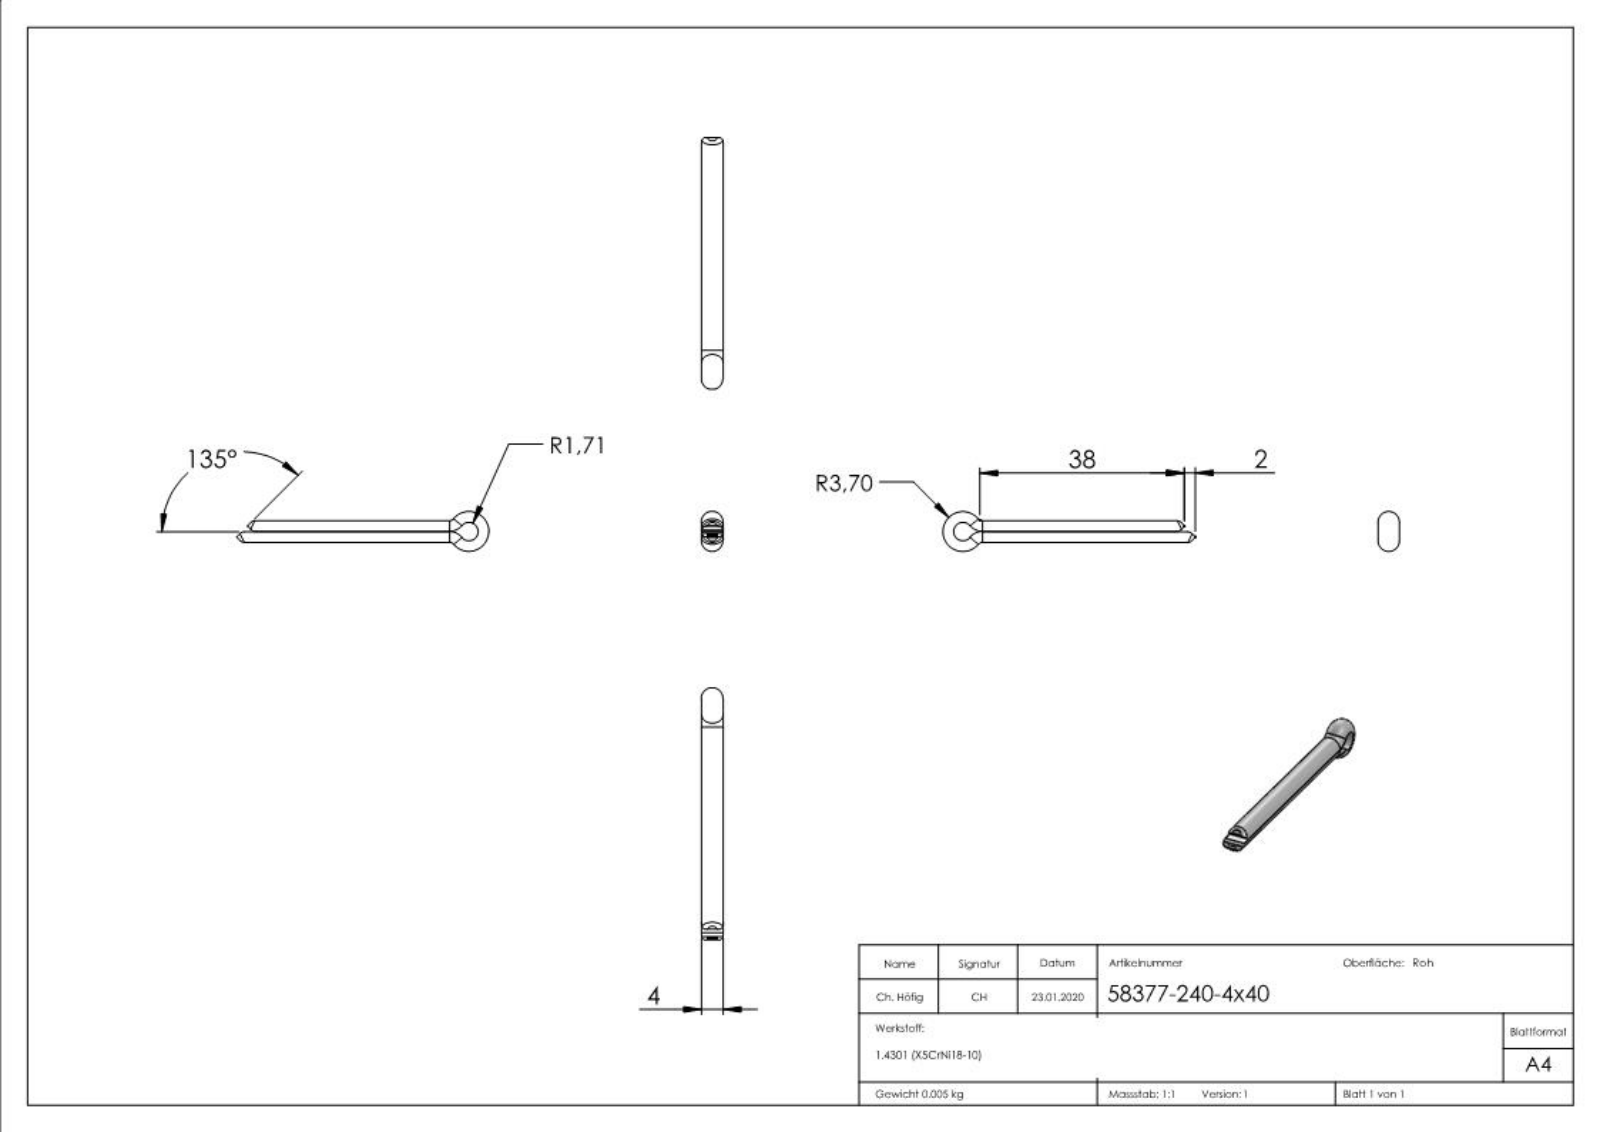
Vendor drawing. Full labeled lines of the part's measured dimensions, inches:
Part name (STEP PRODUCT): 58377-240-4x40
STEP written by: SolidWorks 2015 (CONFIG_CONTROL_DESIGN)
Units: inches
Bodies: 1 solid, 303 faces (180 planar, 7 cylindrical, 116 other)
Overall size (bounding box): 1.843 × 0.291 × 0.157
Volume: 0.035 in³ · Surface area: 1.48 in²
Round bosses / shafts (diameter × count): ⌀0.157 ×1
Partial cylindrical surfaces — rounded edges, fillets, slot ends (radius × count): R0.039 ×2, R0.118 ×2, R0.067 ×1
Main face-to-face distances: 0.113, 0.079, 0.026, 0.023, 0.024, 0.013, 0.043, 0.089, 0.087, 0.022
